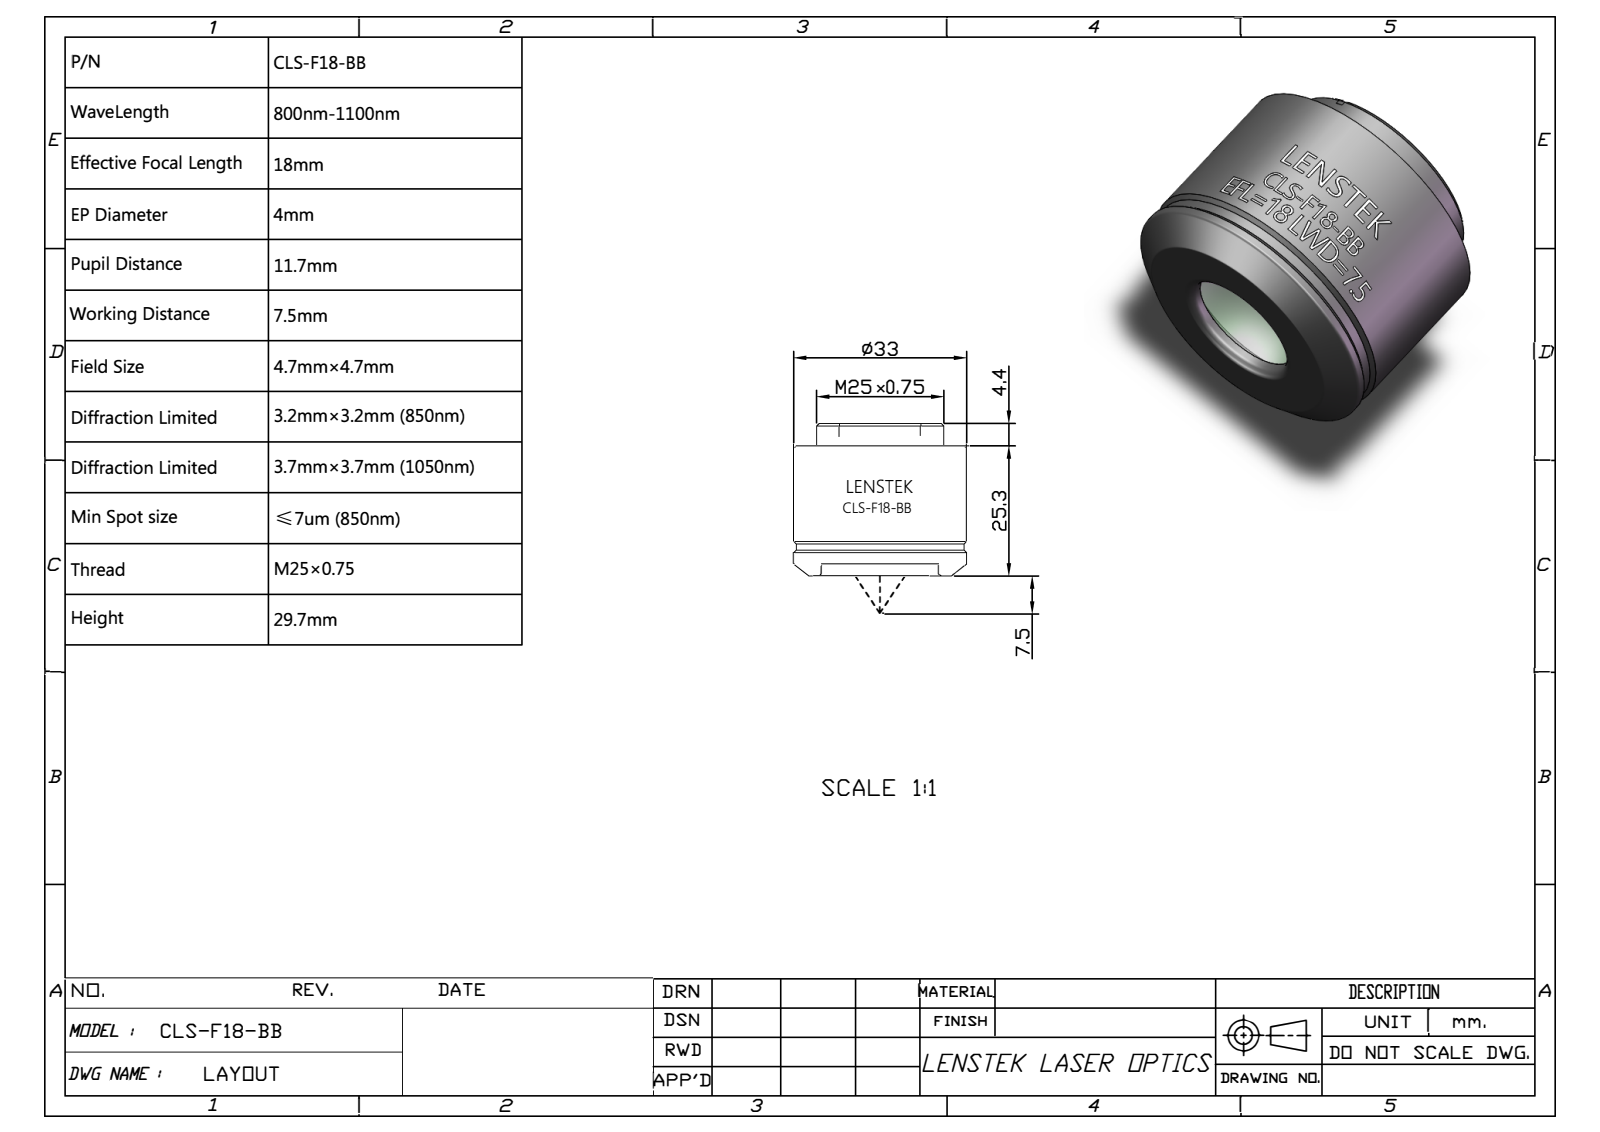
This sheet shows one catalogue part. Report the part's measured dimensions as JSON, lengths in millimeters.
{"part_name": "CLS-F18-BB", "step_written_by": "SolidWorks 2018 (AUTOMOTIVE_DESIGN)", "units": "millimeters", "bodies": {"solids": 7, "faces": 475, "planar": 223, "cylindrical": 83, "other": 169}, "overall_size": [33, 33, 27.5], "volume_mm3": 14058, "surface_area_mm2": 12443, "round_holes": [[14, 1], [18.5, 1], [20.5, 1], [26, 1], [28, 1]], "round_bosses_or_shafts": [[33, 1], [32, 1], [30, 1], [25.5, 1], [25, 1], [24, 1], [18, 1], [17.6, 1]], "partial_cylinders_radius": [[16.49, 1]], "face_to_face_distances": [1.7, 3.7, 3.9, 21.5, 19.9, 3, 6, 25.8, 27.5, 1.5]}
